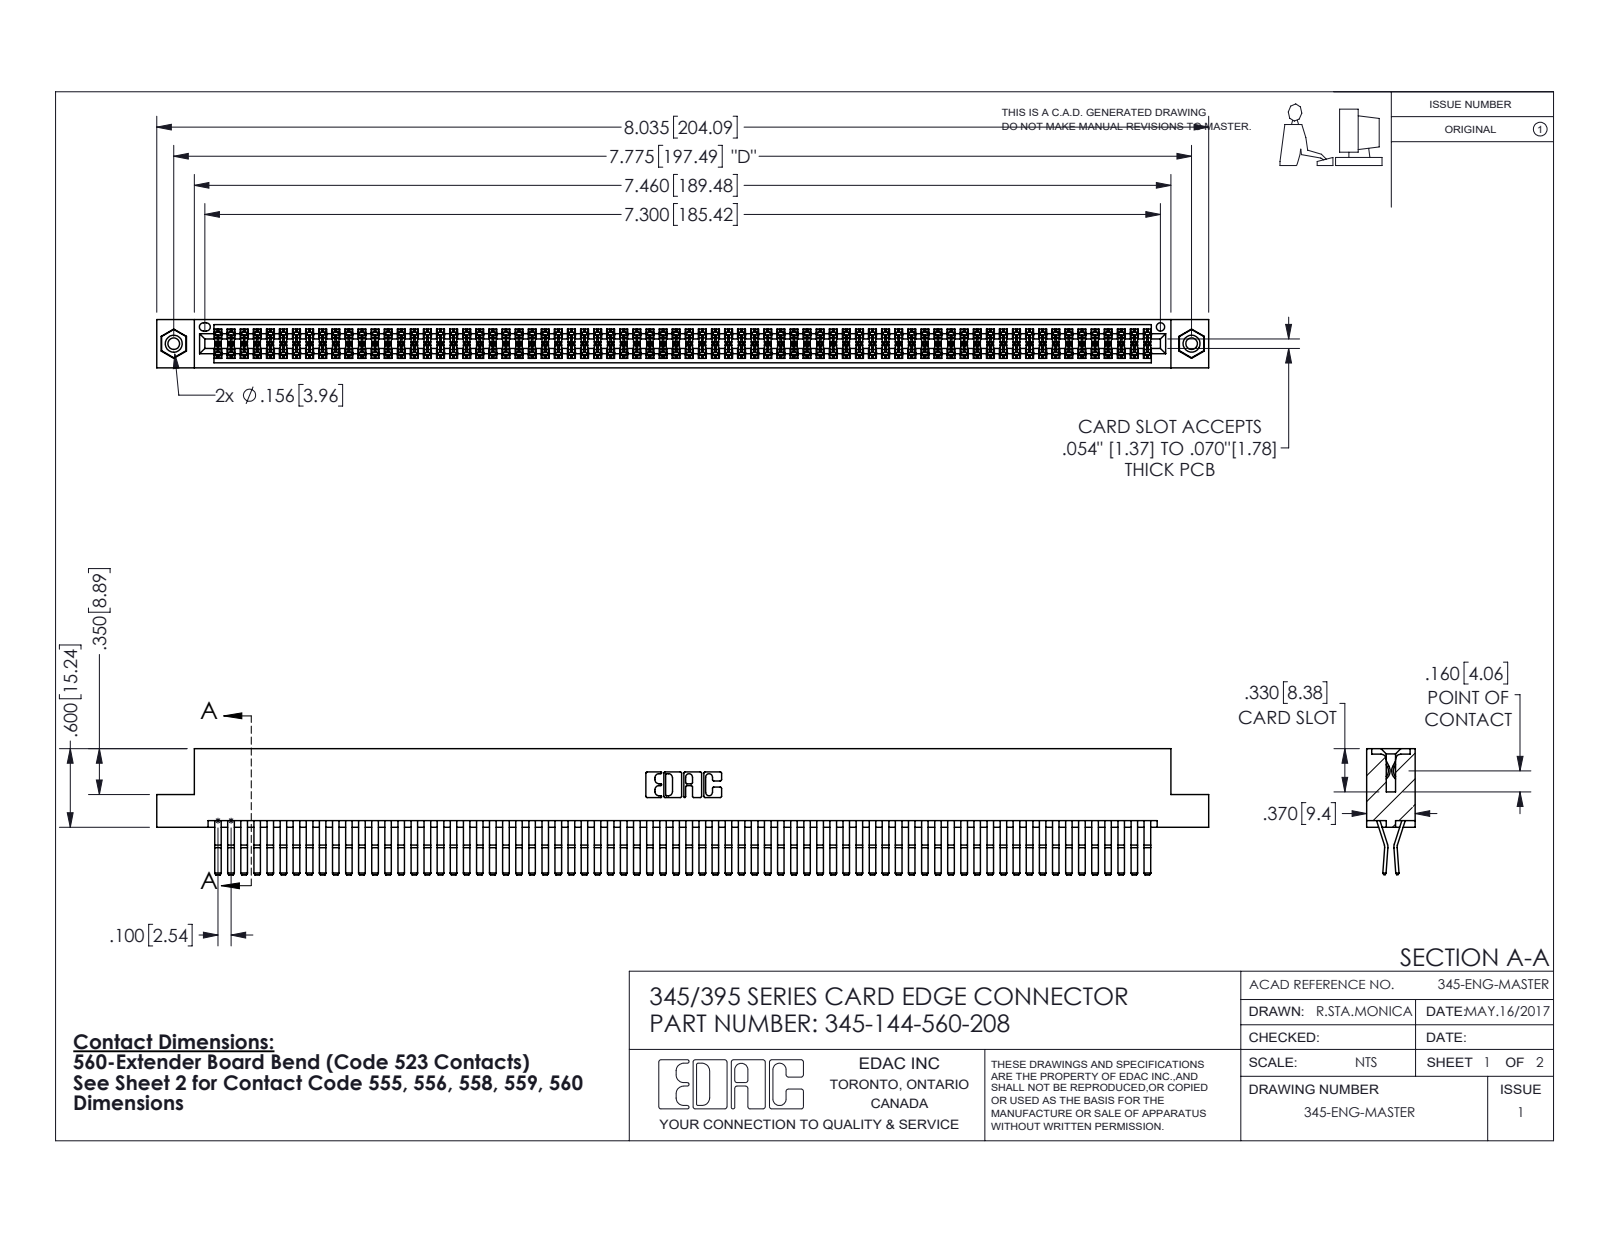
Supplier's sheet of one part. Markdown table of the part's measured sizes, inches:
| quantity | value |
| --- | --- |
| part name | 345-292-001_560 Tail; 345-144-560-208; 345 Part_Flush Mounting Lugs - 0.156 Dia-TI; 345-250-001_345-250-003-102 |
| STEP written by | SolidWorks 2016 (CONFIG_CONTROL_DESIGN) |
| units | inches |
| bodies | 147 solids, 7674 faces (4864 planar, 2794 cylindrical, 16 other) |
| overall size | 8.035 × 0.962 × 0.37 |
| volume | 1.284 in³ |
| surface area | 52.89 in² |
| round holes (diameter × count) | 0.089 × 2, 0.125 × 2, 0.156 × 2, 0.064 × 1 |
| round bosses / shafts (diameter × count) | 0.155 × 2 |
| partial cylindrical surfaces (radius × count) | 0.006 × 217, 0.01 × 22, 0.007 × 6, 0.031 × 6, 0.026 × 3, 0.01 × 2, 0.014 × 2, 0.019 × 2 |
| main face-to-face distances | 0.025, 0.072, 0.298, 0.37, 0.2, 0.098, 0.272, 0.225, 0.175, 0.149 |
| hole center spacings | 0.27, 7.539, 7.775 |
